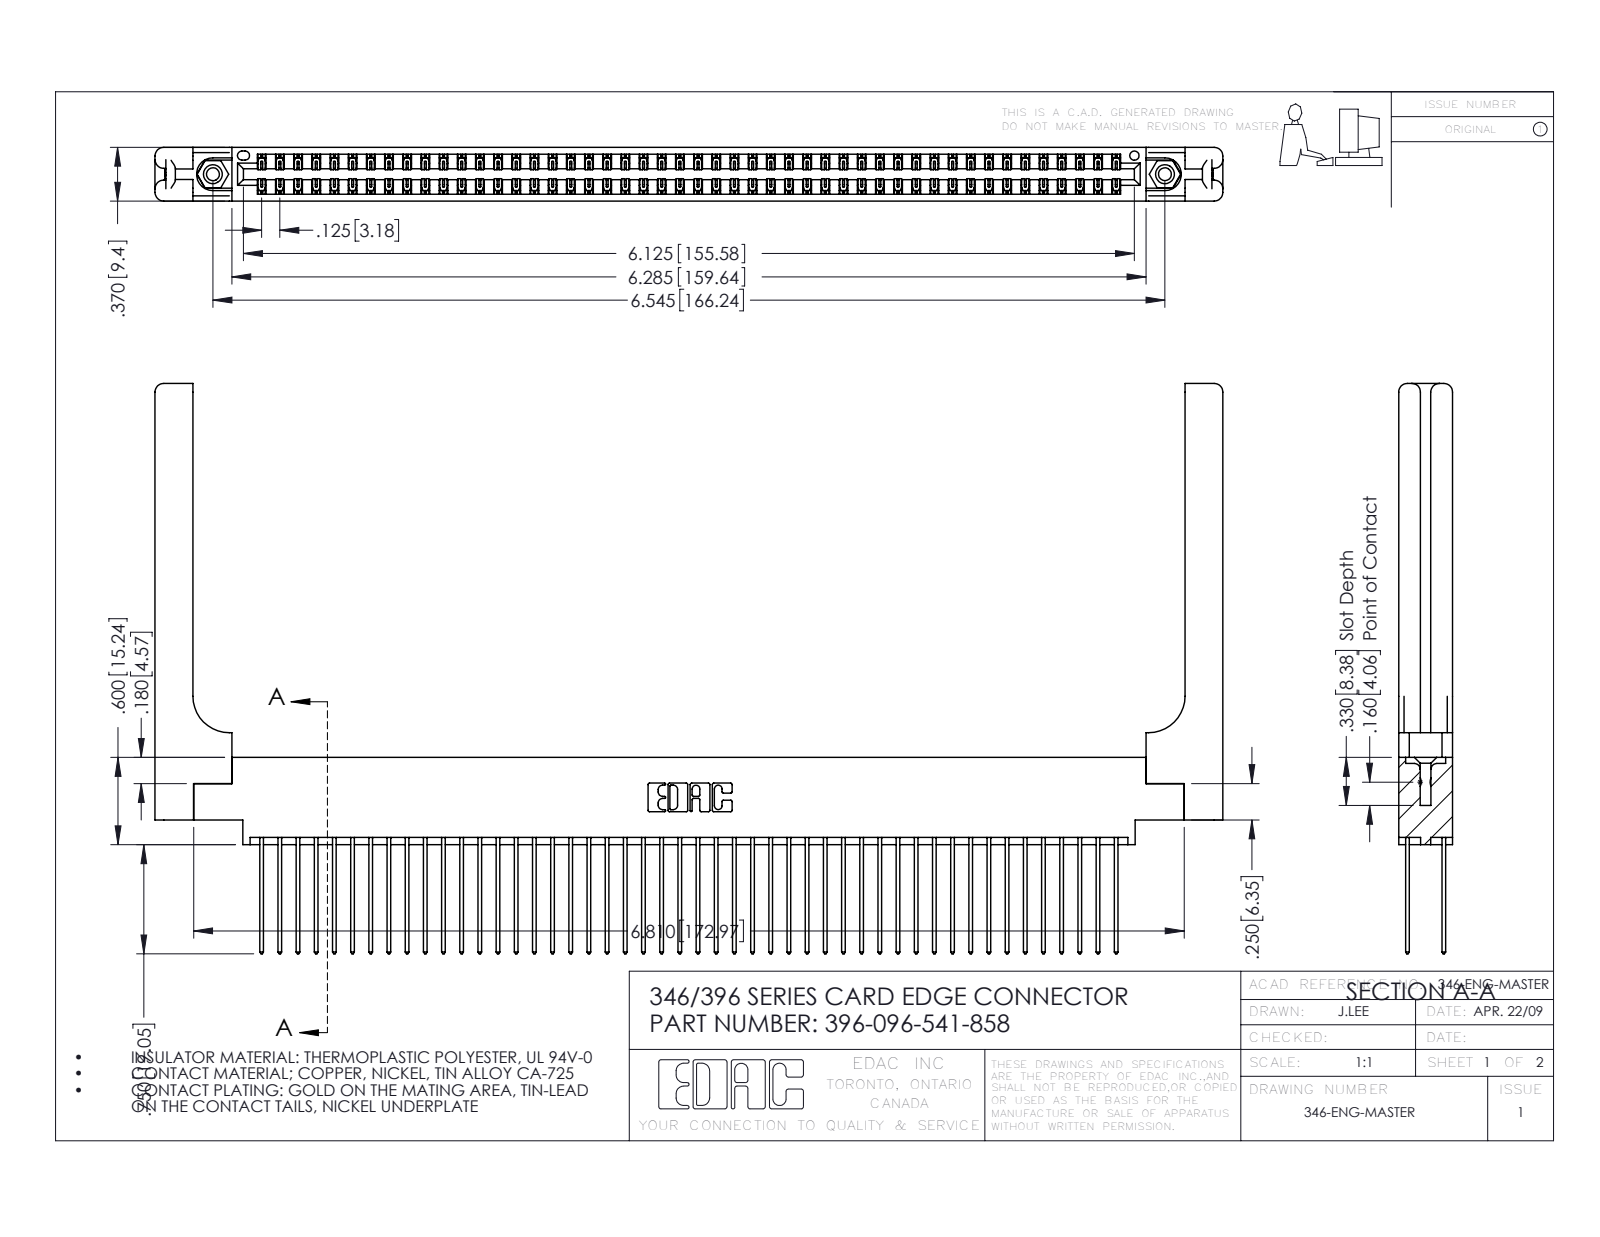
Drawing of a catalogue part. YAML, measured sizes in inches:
part_name: "396-096-541-858; 345-292-001_345-293-141; 345-250-001_345-250-001-102; 346 Part_0.170 Offset - 0.156 Dia-TH (+1 more)"
step_written_by: "SolidWorks 2016 (CONFIG_CONTROL_DESIGN)"
units: inches
bodies: {solids: 101, faces: 5374, planar: 3588, cylindrical: 1726, other: 60}
overall_size: [7.341, 3.92, 0.37]
volume: 1.594
surface_area: 51.91
round_holes:
  - {diameter: 0.089, count: 2}
  - {diameter: 0.125, count: 2}
  - {diameter: 0.156, count: 2}
  - {diameter: 0.064, count: 1}
round_bosses_or_shafts:
  - {diameter: 0.155, count: 2}
partial_cylinders:
  - {radius: 0.006, count: 144}
  - {radius: 0.01, count: 96}
  - {radius: 0.01, count: 22}
  - {radius: 0.06, count: 16}
  - {radius: 0.007, count: 6}
  - {radius: 0.031, count: 6}
  - {radius: 0.026, count: 3}
  - {radius: 0.014, count: 2}
face_to_face_distances: [0.048, 0.322, 0.072, 0.37, 0.25, 0.025, 0.298, 0.275, 0.148, 0.15]
hole_center_spacings: [0.246, 6.336, 6.545]
